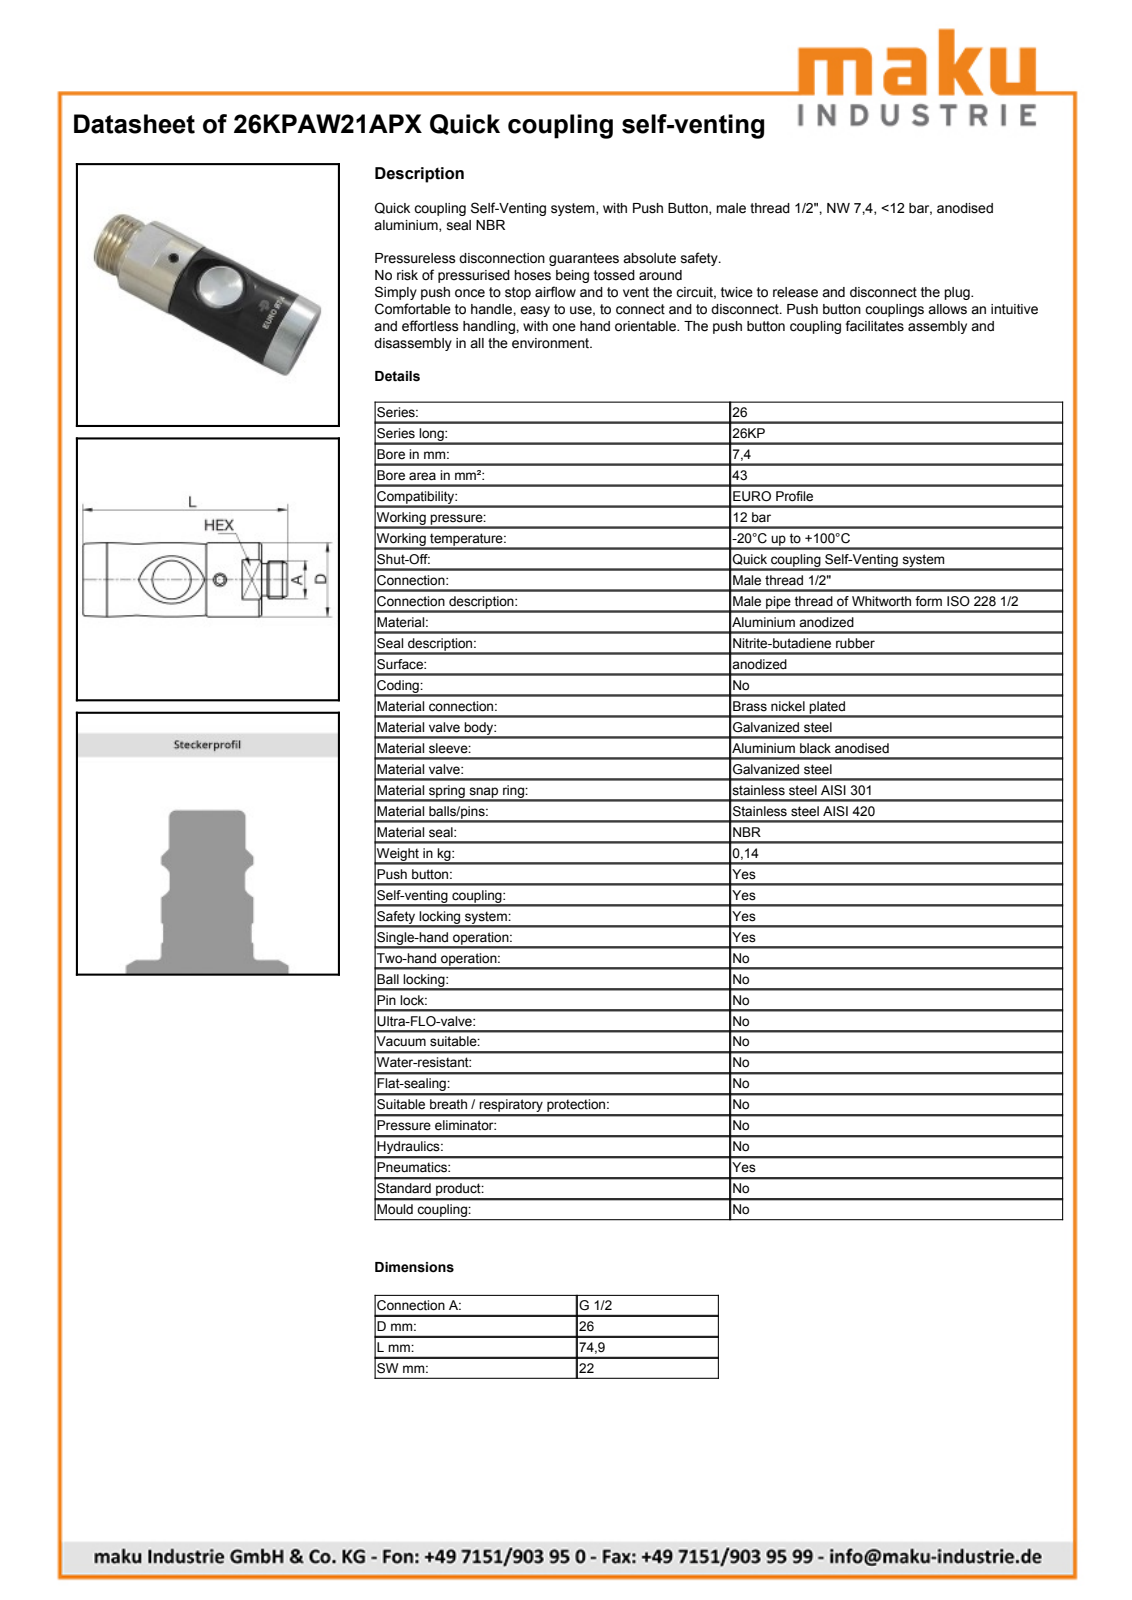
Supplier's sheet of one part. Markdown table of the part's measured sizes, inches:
| quantity | value |
| --- | --- |
| part name | 26KPAW21APX |
| STEP written by | Autodesk Inventor 2019 (AUTOMOTIVE_DESIGN) |
| units | inches |
| bodies | 39 solids, 259 faces (72 planar, 86 cylindrical, 101 other) |
| overall size | 2.949 × 1.024 × 1.024 |
| volume | 2.513 in³ |
| surface area | 39.94 in² |
| round holes (diameter × count) | 0.488 × 2, 0.138 × 1, 0.256 × 1, 0.276 × 1, 0.38 × 1, 0.398 × 1, 0.417 × 1, 0.476 × 1, 0.482 × 1, 0.504 × 1, 0.535 × 1, 0.551 × 1 |
| round bosses / shafts (diameter × count) | 1.024 × 1, 0.866 × 1, 0.837 × 1, 0.713 × 1, 0.701 × 1, 0.65 × 1, 0.641 × 1, 0.622 × 1 |
| partial cylindrical surfaces (radius × count) | 0.244 × 2, 0.173 × 1 |
| main face-to-face distances | 1.709, 0.331, 1.378, 1.24, 2.618, 2.949, 0.472, 0.768, 2.146, 2.476 |
| hole center spacings | 0.024, 0.028, 0.051, 0.671 |
